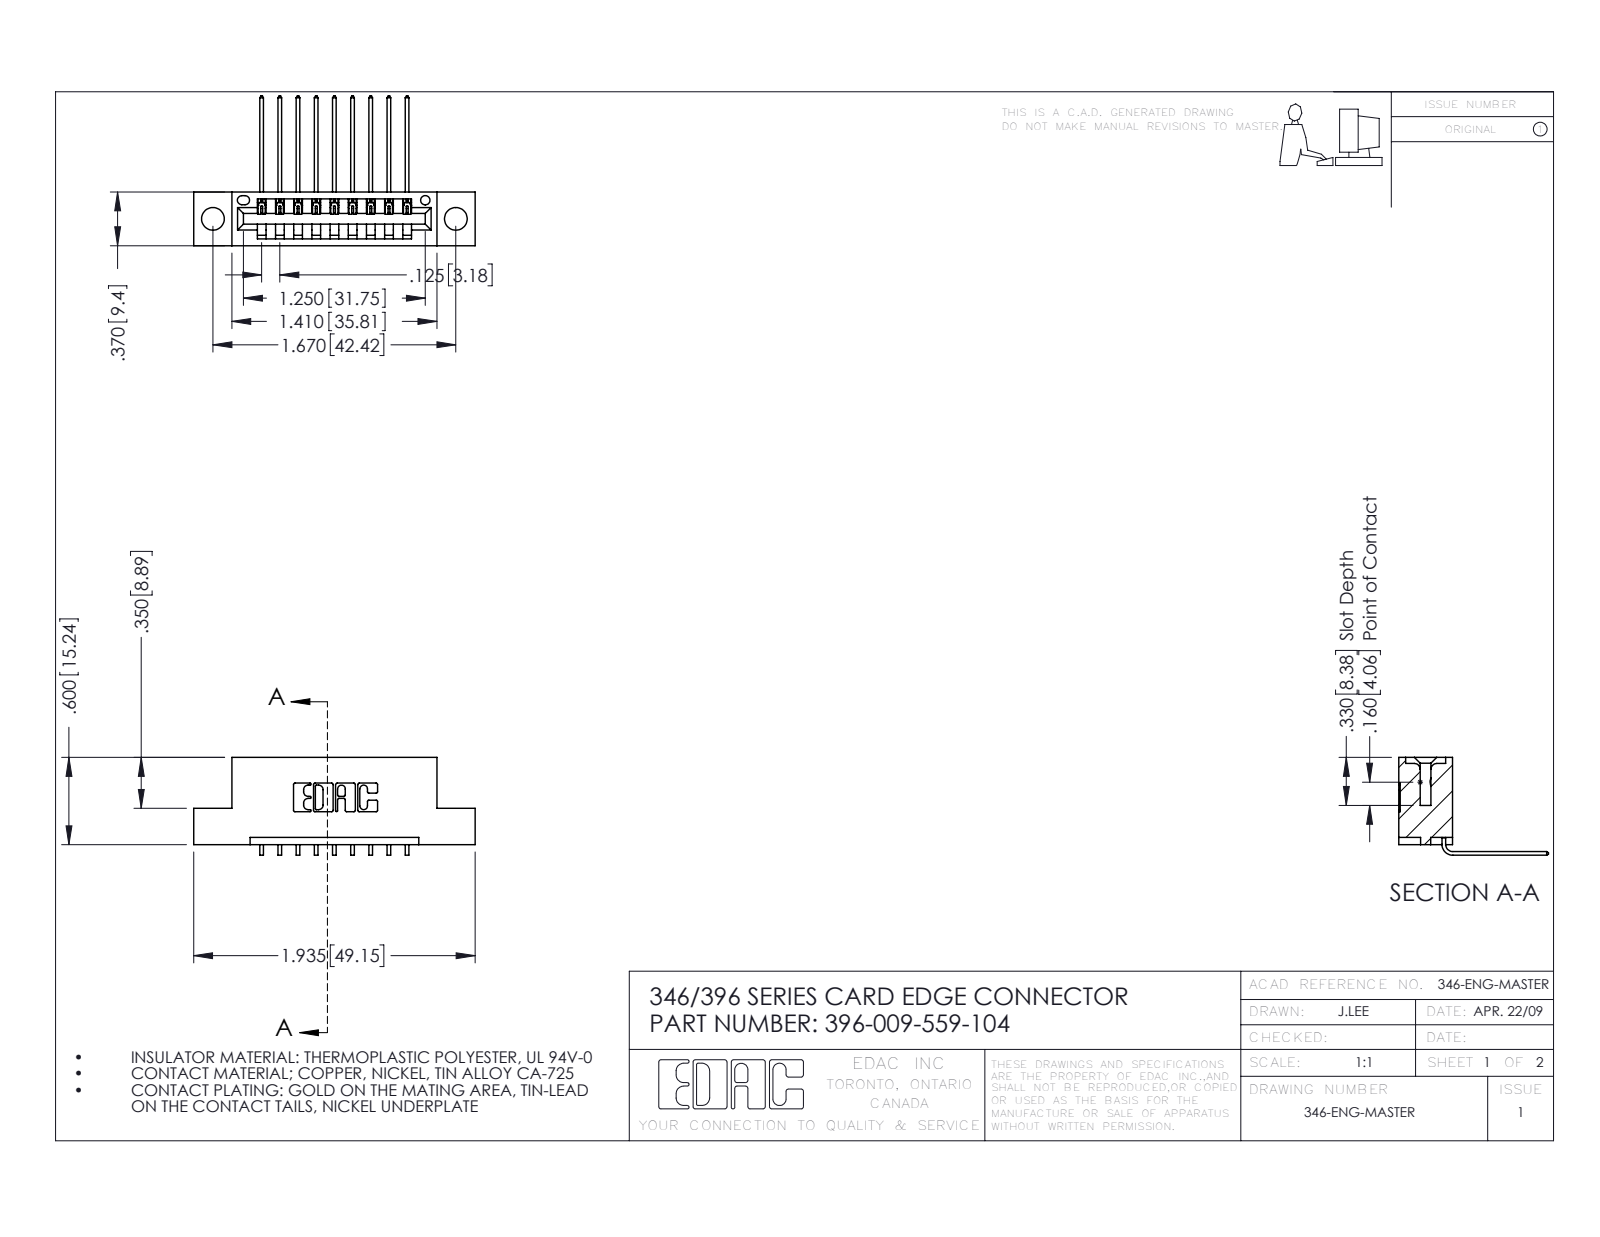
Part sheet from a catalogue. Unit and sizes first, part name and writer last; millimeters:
Units: millimetres
Overall size (bounding box): 49.1 × 26.2 × 17.1
Round holes (diameter × count): ⌀4 ×2, ⌀1.6 ×1
Partial cylindrical surfaces — rounded edges, fillets, slot ends (radius × count): R0.3 ×22, R0.2 ×18, R0.2 ×6, R0.8 ×6, R0.7 ×3, R0.8 ×2, R1 ×2, R0.4 ×1
Main face-to-face distances: 6.4, 1.2, 8.2, 9.4, 1.8, 7.6, 0.6, 3.8, 5.6, 2.5
Hole centre spacings: 6.2, 37.2, 42.4
Volume: 4 420 mm³ · Surface area: 5 152 mm²
Bodies: 10 solids, 662 faces (454 planar, 208 cylindrical, 0 other)
Part name (STEP PRODUCT): 346 Part_Flush Mounting Lugs - 0.156 Dia-TH; 396-009-559-104; 345-292-001_558 559 Tail - 1
STEP written by: SolidWorks 2016 (CONFIG_CONTROL_DESIGN)
